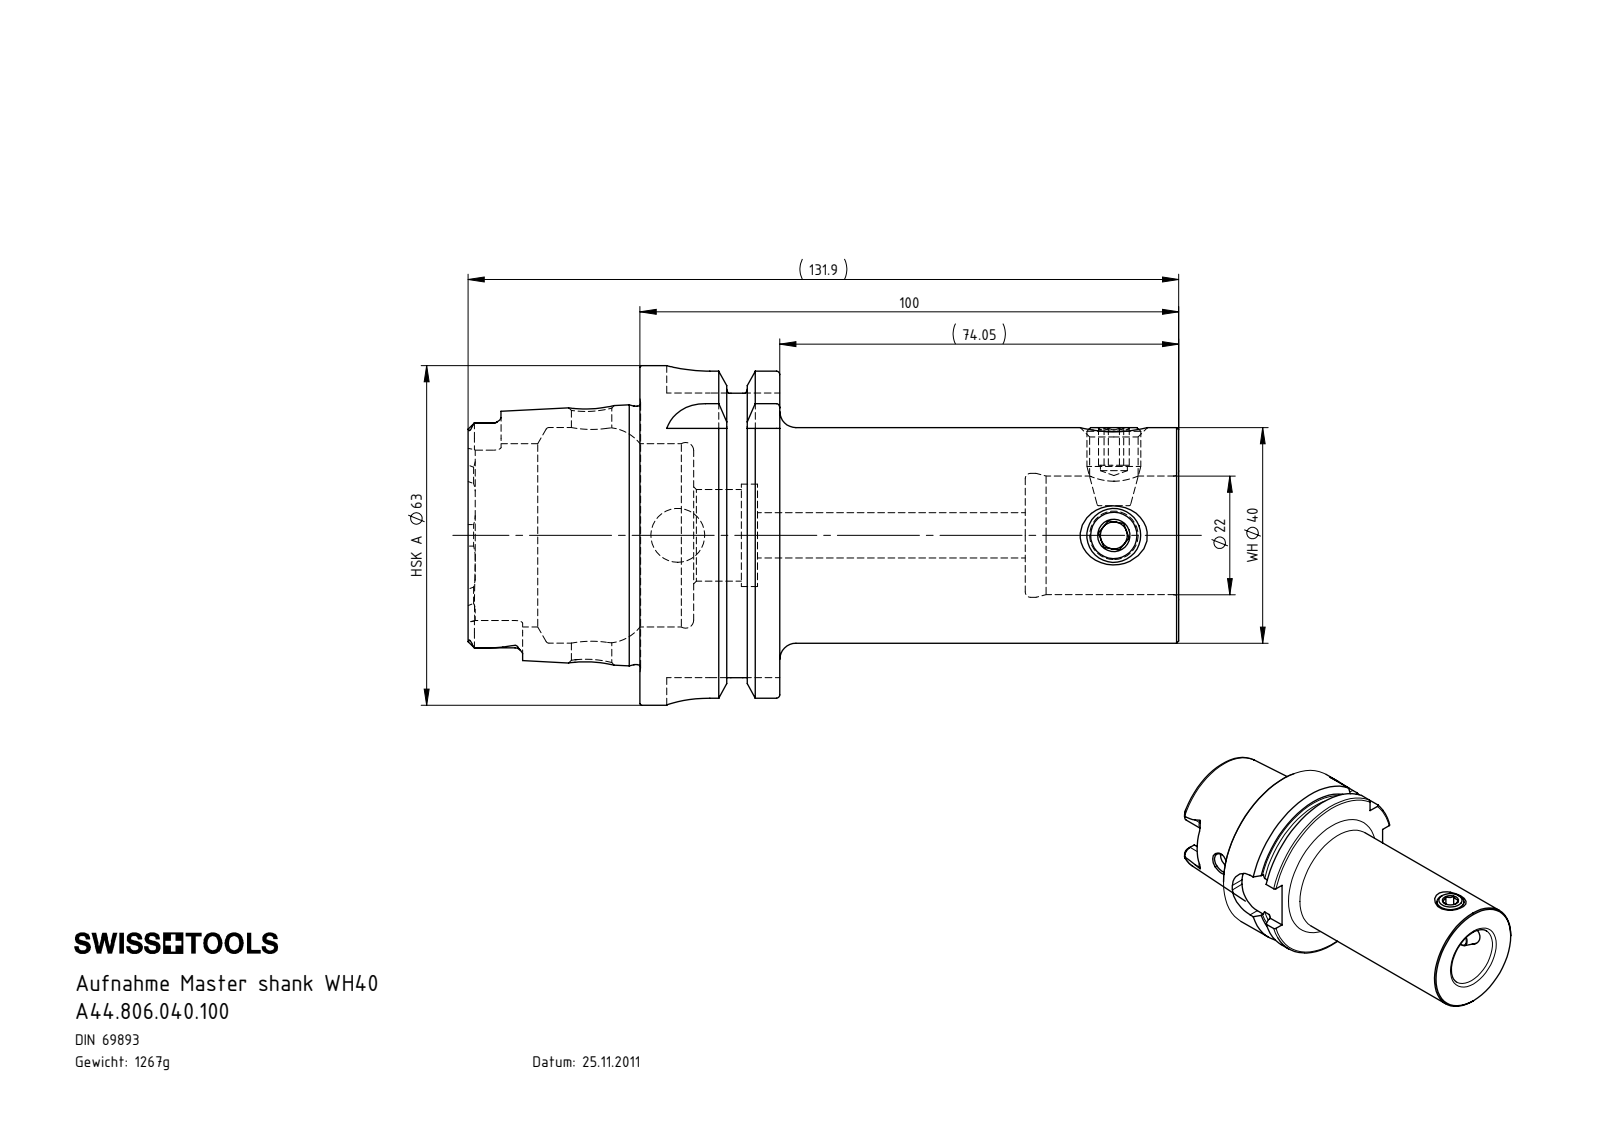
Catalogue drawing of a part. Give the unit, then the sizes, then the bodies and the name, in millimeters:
Units: millimetres
Overall size (bounding box): 131.9 × 63 × 63
Round holes (diameter × count): ⌀5 ×2, ⌀9 ×2, ⌀7.5 ×1, ⌀8.4 ×1, ⌀10 ×1, ⌀17 ×1, ⌀19 ×1, ⌀22 ×1, ⌀23 ×1, ⌀34 ×1, ⌀40 ×1
Round bosses / shafts (diameter × count): ⌀10 ×2, ⌀63 ×1, ⌀54.95 ×1, ⌀47.94 ×1
Partial cylindrical surfaces — rounded edges, fillets, slot ends (radius × count): R1.4 ×6, R2.88 ×4, R8 ×4
Main face-to-face distances: 25.95, 100, 74.05, 16, 9.95, 90.05, 31.9, 41.85, 57.85, 131.9
Hole centre spacings: 80.95, 96.95
Volume: 161 361 mm³ · Surface area: 35 996 mm²
Bodies: 3 solids, 241 faces (75 planar, 61 cylindrical, 105 other)
Part name (STEP PRODUCT): HA6-WH4.K01.100_B; WH4-ER1.001.015; A44.806.040.100
STEP written by: SolidWorks 2017 (CONFIG_CONTROL_DESIGN)
